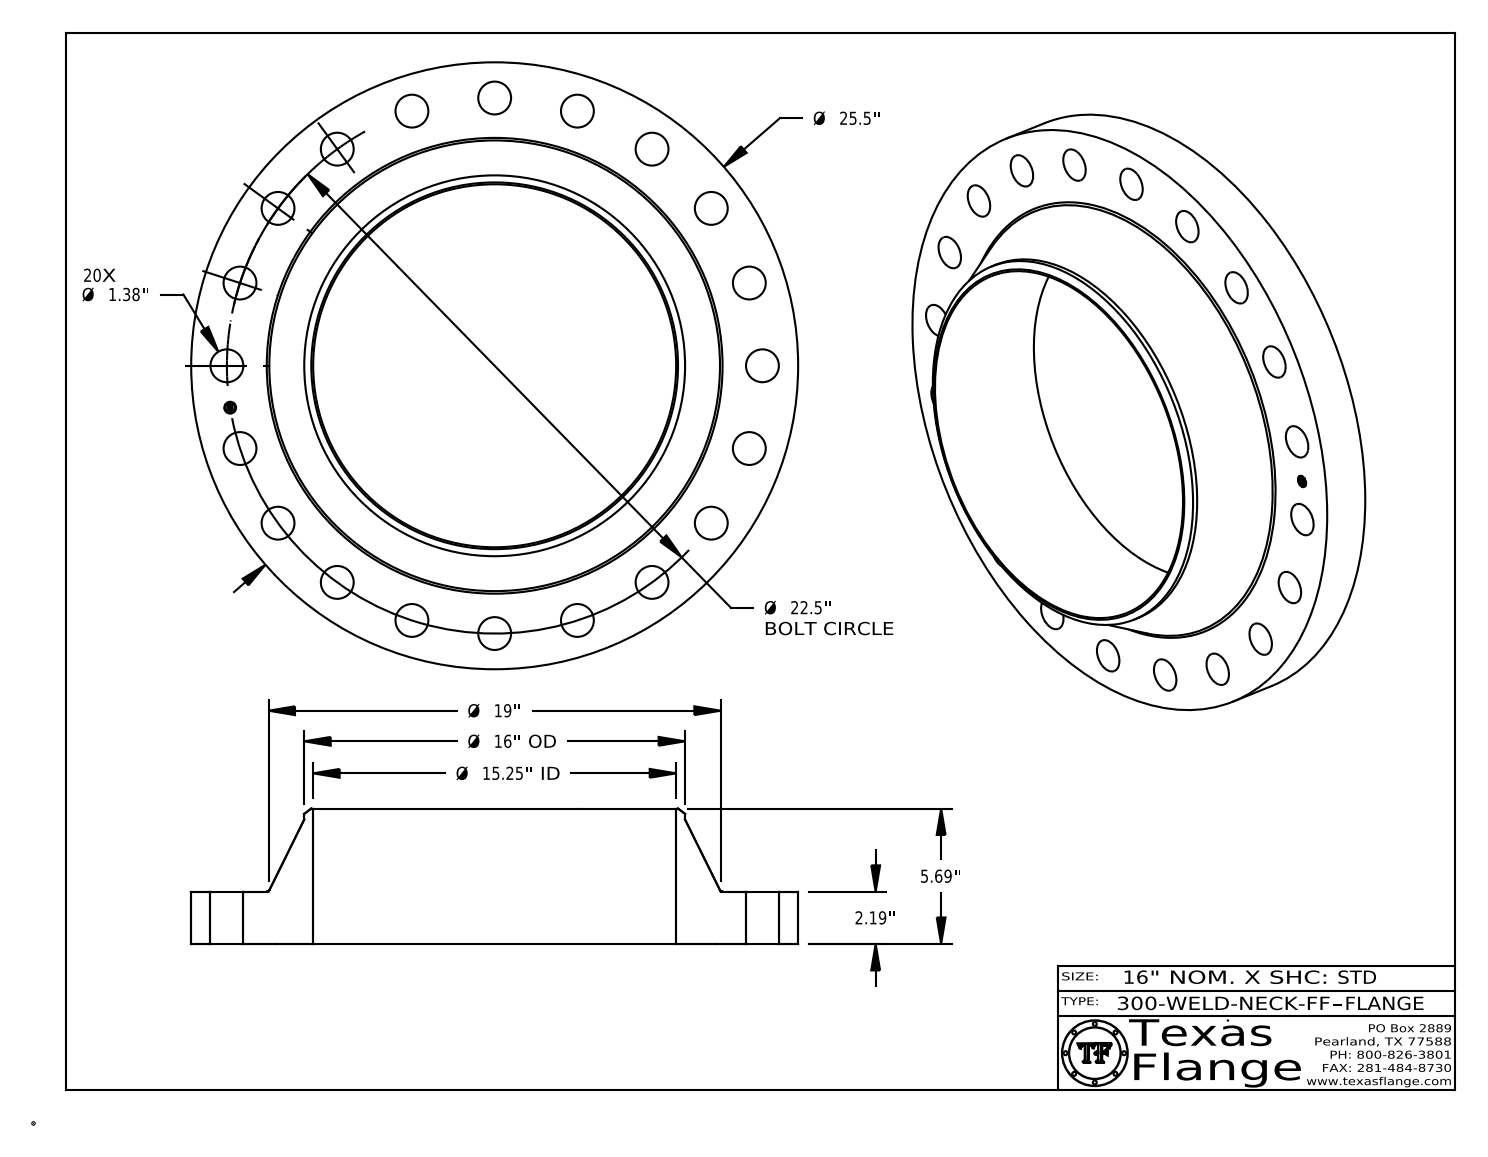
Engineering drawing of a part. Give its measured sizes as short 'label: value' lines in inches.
name: 300-WELD-NECK-FF
written by: CATIA V5 STEP AP214 (AUTOMOTIVE_DESIGN)
unit: in
bodies: 1 solid, 441 faces (369 planar, 66 cylindrical, 6 other)
size: 25.5 × 25.5 × 5.69
volume: 837.4 in³; area: 1 353 in²
holes: 20× ⌀1.38, 1× ⌀0.495, 1× ⌀15.25
bosses: 8× ⌀0.03, 1× ⌀25.5, 1× ⌀16, 1× ⌀0.39
face distances: 2.19, 5.69, 3.5, 2.175, 0.015, 3.515, 0.148, 0.145, 0.027, 0.096
hole spacings: 11.25, 6.953, 13.225, 3.52, 18.203, 20.048, 21.399, 22.223
